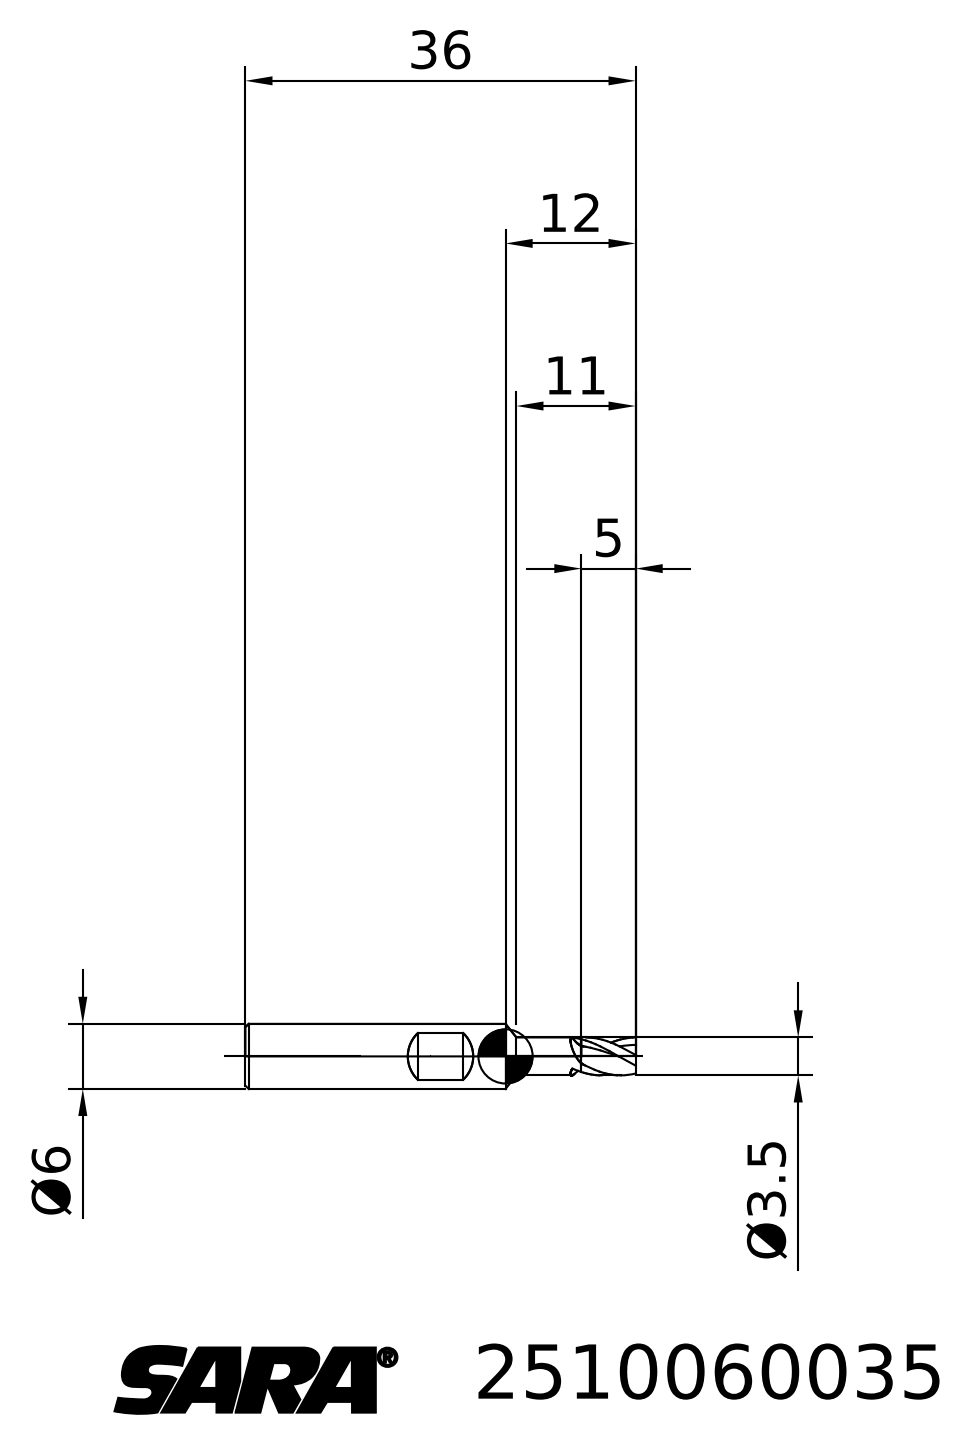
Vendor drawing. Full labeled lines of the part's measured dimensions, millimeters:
STEP written by: TDM (AUTOMOTIVE_DESIGN)
Units: millimetres
Bodies: 2 solids, 27 faces (7 planar, 0 cylindrical, 20 other)
Overall size (bounding box): 36 × 6 × 6
Volume: 765 mm³ · Surface area: 643 mm²
Main face-to-face distances: 31, 5, 36
